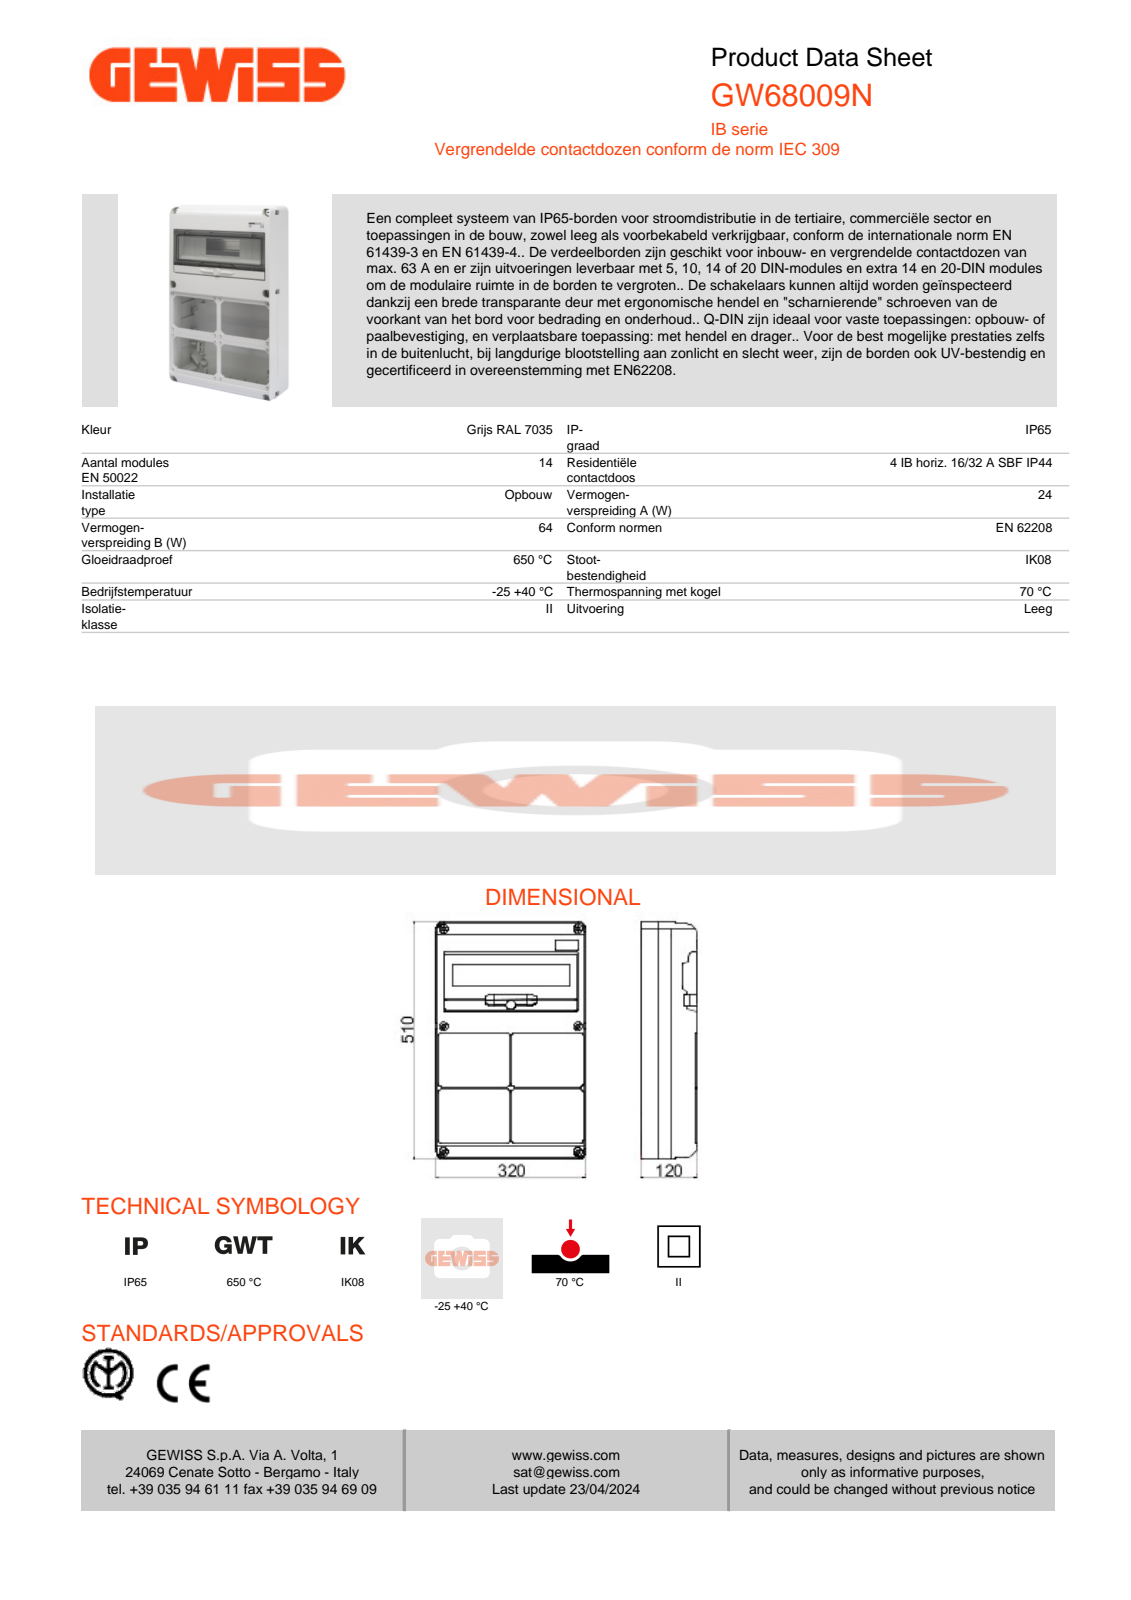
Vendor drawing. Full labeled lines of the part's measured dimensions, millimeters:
Part name (STEP PRODUCT): 55523450_FONDO_14_MOD_2_GRANDEZ; 55523468G_FRONTALE_14M_2GRAND_4; GW68009N_ASM
STEP written by: CREO PARAMETRIC BY PTC INC, 2020354 (CONFIG_CONTROL_DESIGN)
Units: millimetres
Bodies: 2 solids, 1055 faces (631 planar, 134 cylindrical, 290 other)
Overall size (bounding box): 510.75 × 321.24 × 124.49
Volume: 2 991 000 mm³ · Surface area: 1 039 000 mm²
Partial cylindrical surfaces — rounded edges, fillets, slot ends (radius × count): R1.5 ×27, R2 ×16, R3.5 ×12, R1 ×8, R1.3 ×8, R0.5 ×6, R13 ×6, R3 ×4
Main face-to-face distances: 3, 115.3, 118.3, 6.5, 108.8, 320.01, 112.3, 313.75, 313.69, 309.69
